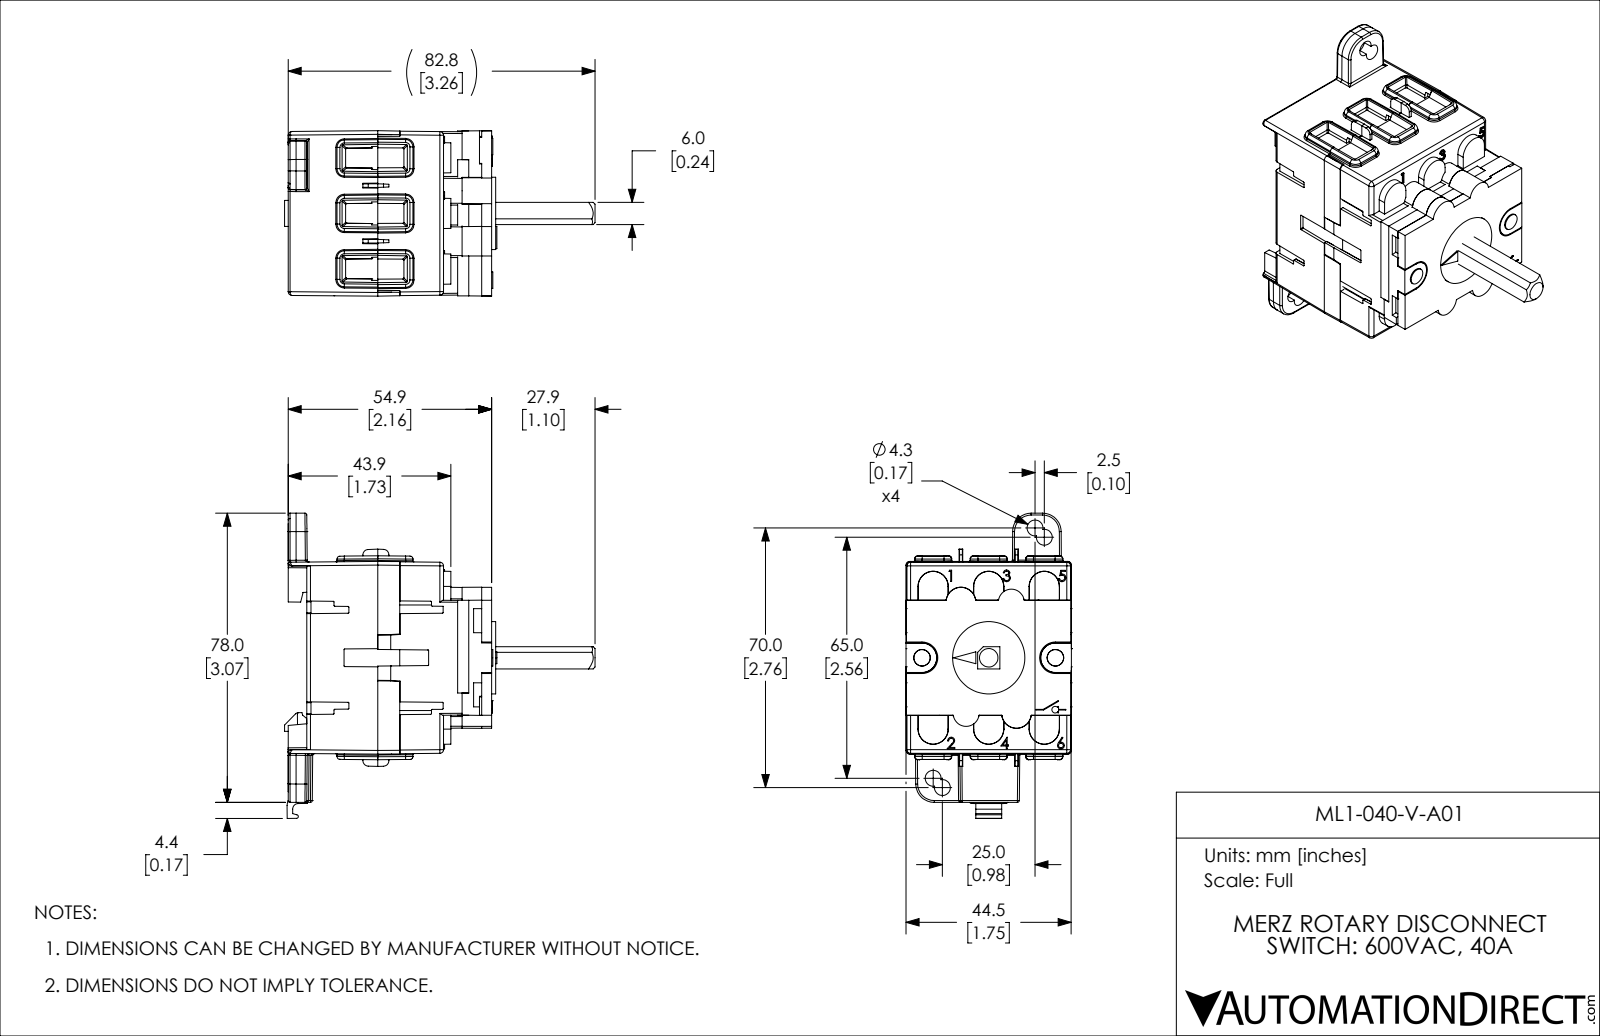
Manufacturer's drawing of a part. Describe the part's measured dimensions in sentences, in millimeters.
The part is named "ML1-040-V-A01". Its 3-D file was written by "SolidWorks 2019 (AUTOMOTIVE_DESIGN)". It is 7 solids with 1402 faces: 776 planar, 412 cylindrical and 214 other. Overall it measures 83.8 by 82.3 by 44.6 millimeters. Its volume is 124 200 cubic millimeters and its surface area 35 010 square millimeters. Round holes: 4 of diameter 4.3, 1 of diameter 8. Round bosses or shafts: 2 of diameter 7, 1 of diameter 19.5, 1 of diameter 16.4, 1 of diameter 12, 1 of diameter 8.5, 1 of diameter 8, 1 of diameter 3. Partial cylindrical surfaces (rounded edges, fillets, slot ends): 75 of radius 0.2, 62 of radius 0.3, 47 of radius 0.5, 29 of radius 1, 28 of radius 0.8, 12 of radius 0.3, 12 of radius 2, 6 of radius 5. The main face-to-face distances are 5.9, 28, 22.1, 41.9, 25.1, 19.2, 47.2, 5.3, 22.8, 16.8. The hole center spacings are 3.5, 72.9, 28.3, 28.5, 48.1, 50.2, 71.6, 74.3.
